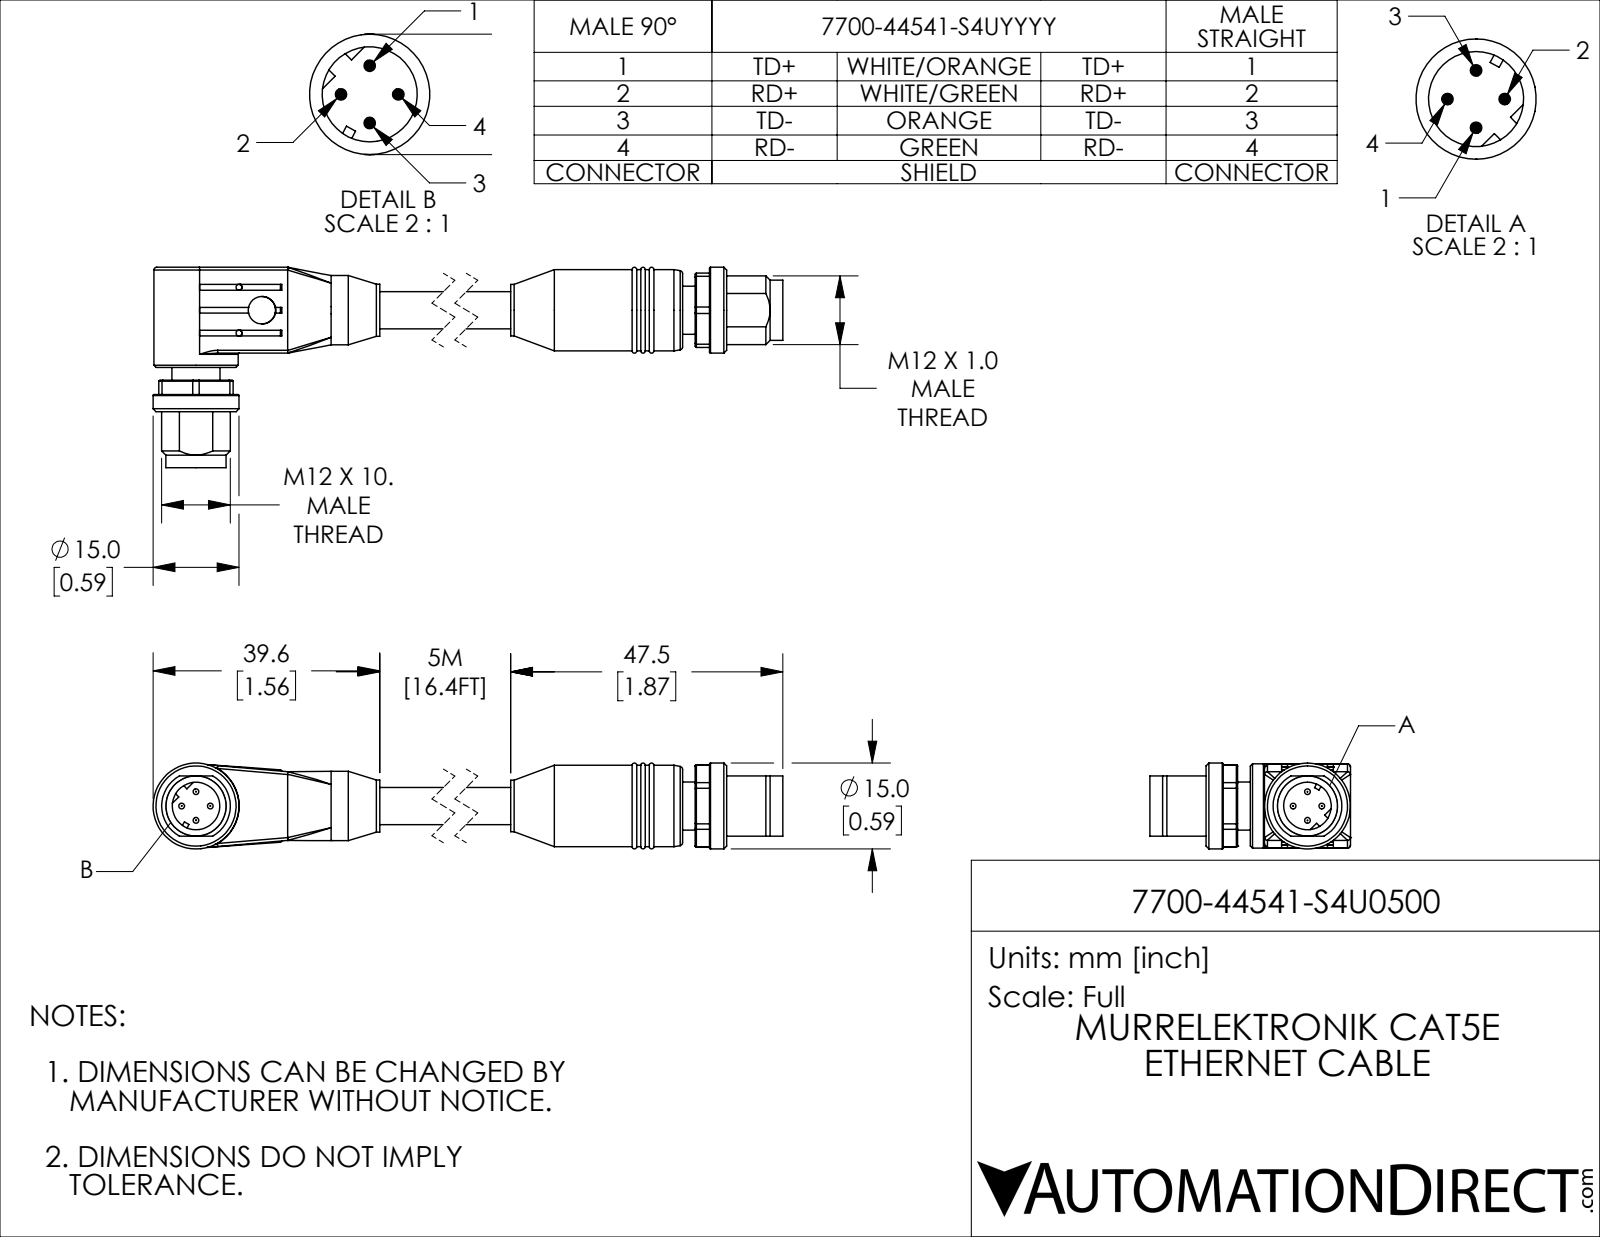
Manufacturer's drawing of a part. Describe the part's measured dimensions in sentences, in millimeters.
The part is named "7700-44541-S4U0500; 7700-44541-S4U0500_1; 7700-44541-S4U0500_2". Its 3-D file was written by "SolidWorks 2021 (CONFIG_CONTROL_DESIGN)". It is 2 solids with 284 faces: 114 planar, 90 cylindrical and 80 other. Overall it measures 133.5 by 35 by 15 millimeters. Its volume is 15 600 cubic millimeters and its surface area 7 045 square millimeters. Round holes: 4 of diameter 1, 2 of diameter 8.3, 1 of diameter 4.8. Round bosses or shafts: 8 of diameter 1, 2 of diameter 15, 2 of diameter 10.5, 2 of diameter 8.4, 1 of diameter 14.7, 1 of diameter 14.2, 1 of diameter 12.1, 1 of diameter 9.1. Partial cylindrical surfaces (rounded edges, fillets, slot ends): 4 of radius 0.5, 2 of radius 0.3, 2 of radius 6, 2 of radius 7.2. The main face-to-face distances are 17.5, 2.2, 2.5, 4.7, 15, 0.9, 6.4, 8.6, 5.5, 7.7. The hole center spacings are 8.
